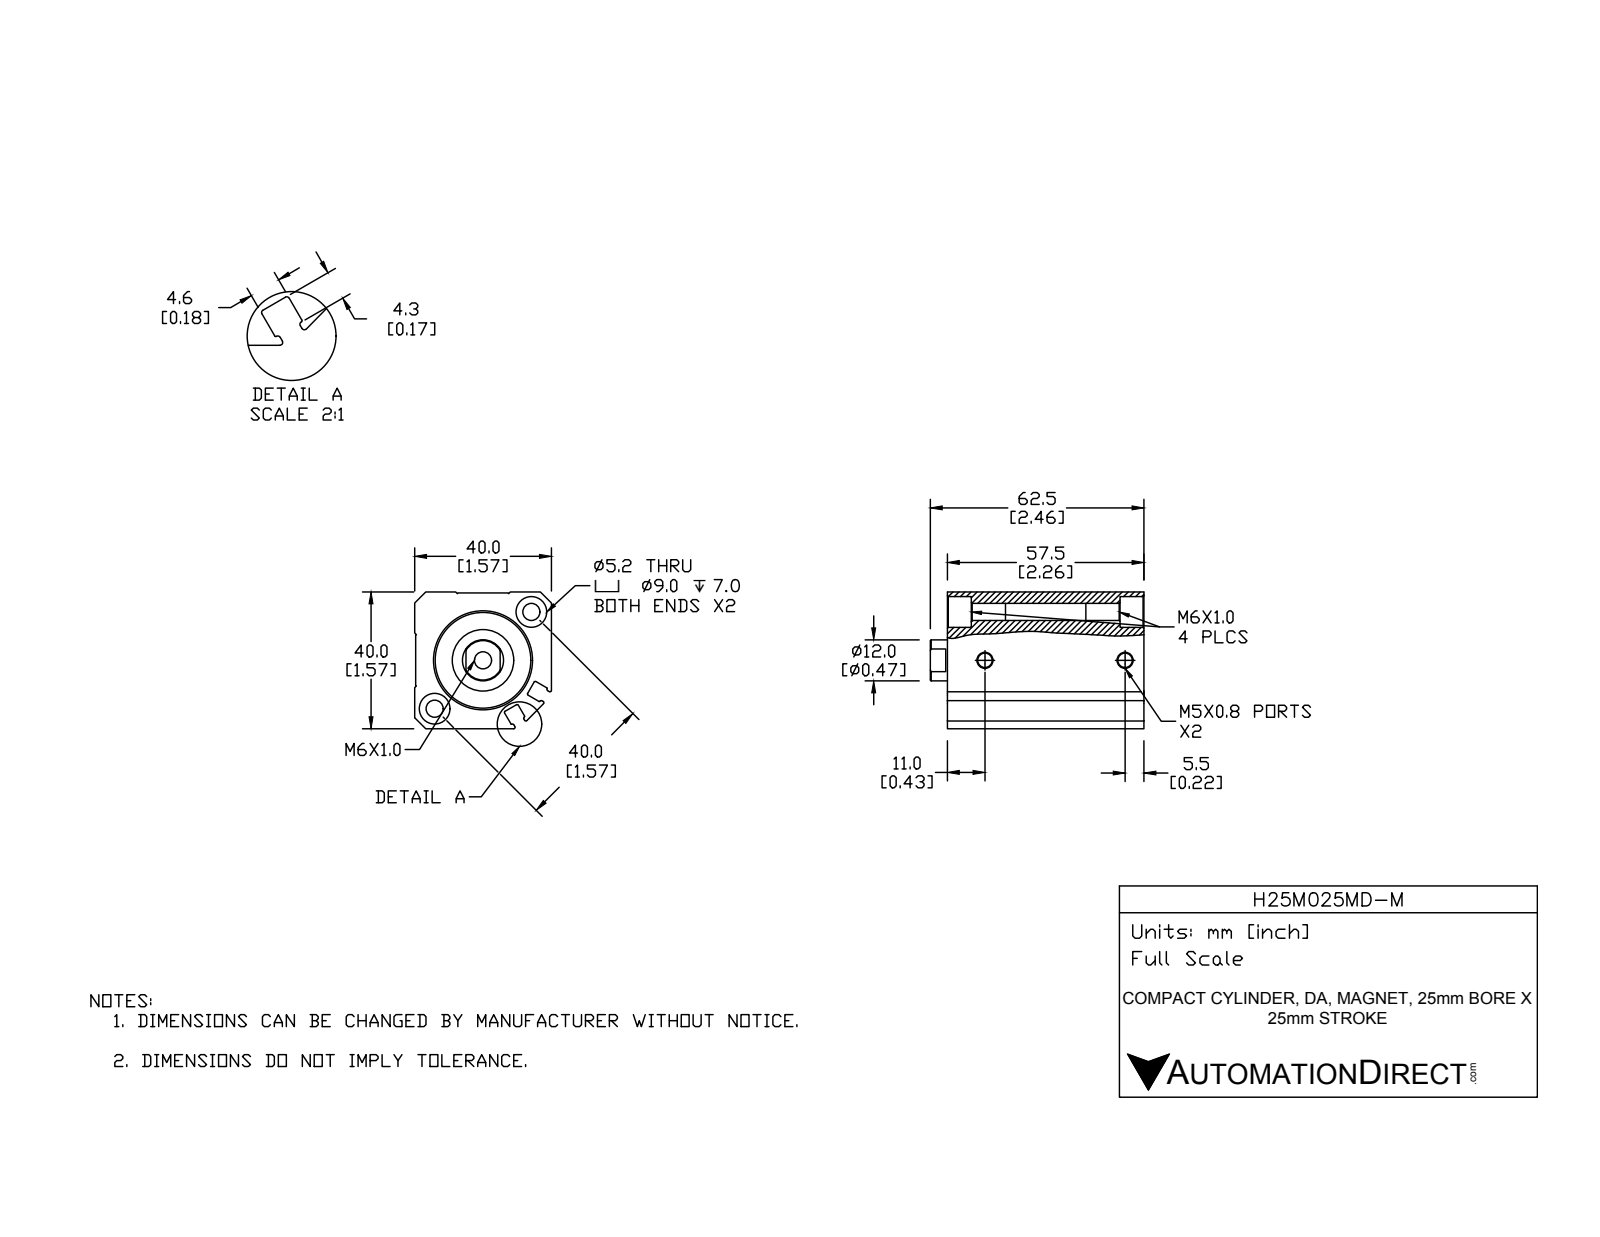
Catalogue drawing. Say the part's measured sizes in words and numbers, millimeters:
The part is named "H25M025MD-M-PISTON; H25M025MD-M-BODY; H25M025MD-M". Its 3-D file was written by "SolidWorks 2015 (CONFIG_CONTROL_DESIGN)". It is 2 solids with 141 faces: 53 planar, 55 cylindrical and 33 other. Overall it measures 62.5 by 40 by 40 millimeters. Its volume is 69 877 cubic millimeters and its surface area 24 243 square millimeters. Round holes: 3 of diameter 5, 2 of diameter 4.2, 2 of diameter 9, 1 of diameter 12, 1 of diameter 16, 1 of diameter 25, 1 of diameter 28. Round bosses or shafts: 1 of diameter 18, 1 of diameter 14. Partial cylindrical surfaces (rounded edges, fillets, slot ends): 12 of radius 0.4, 4 of radius 0.2. The main face-to-face distances are 40, 39.7, 4, 57.5, 53.5, 1.4, 2.6, 56.1, 46.5, 4.6. The hole center spacings are 20, 39.99, 41.
